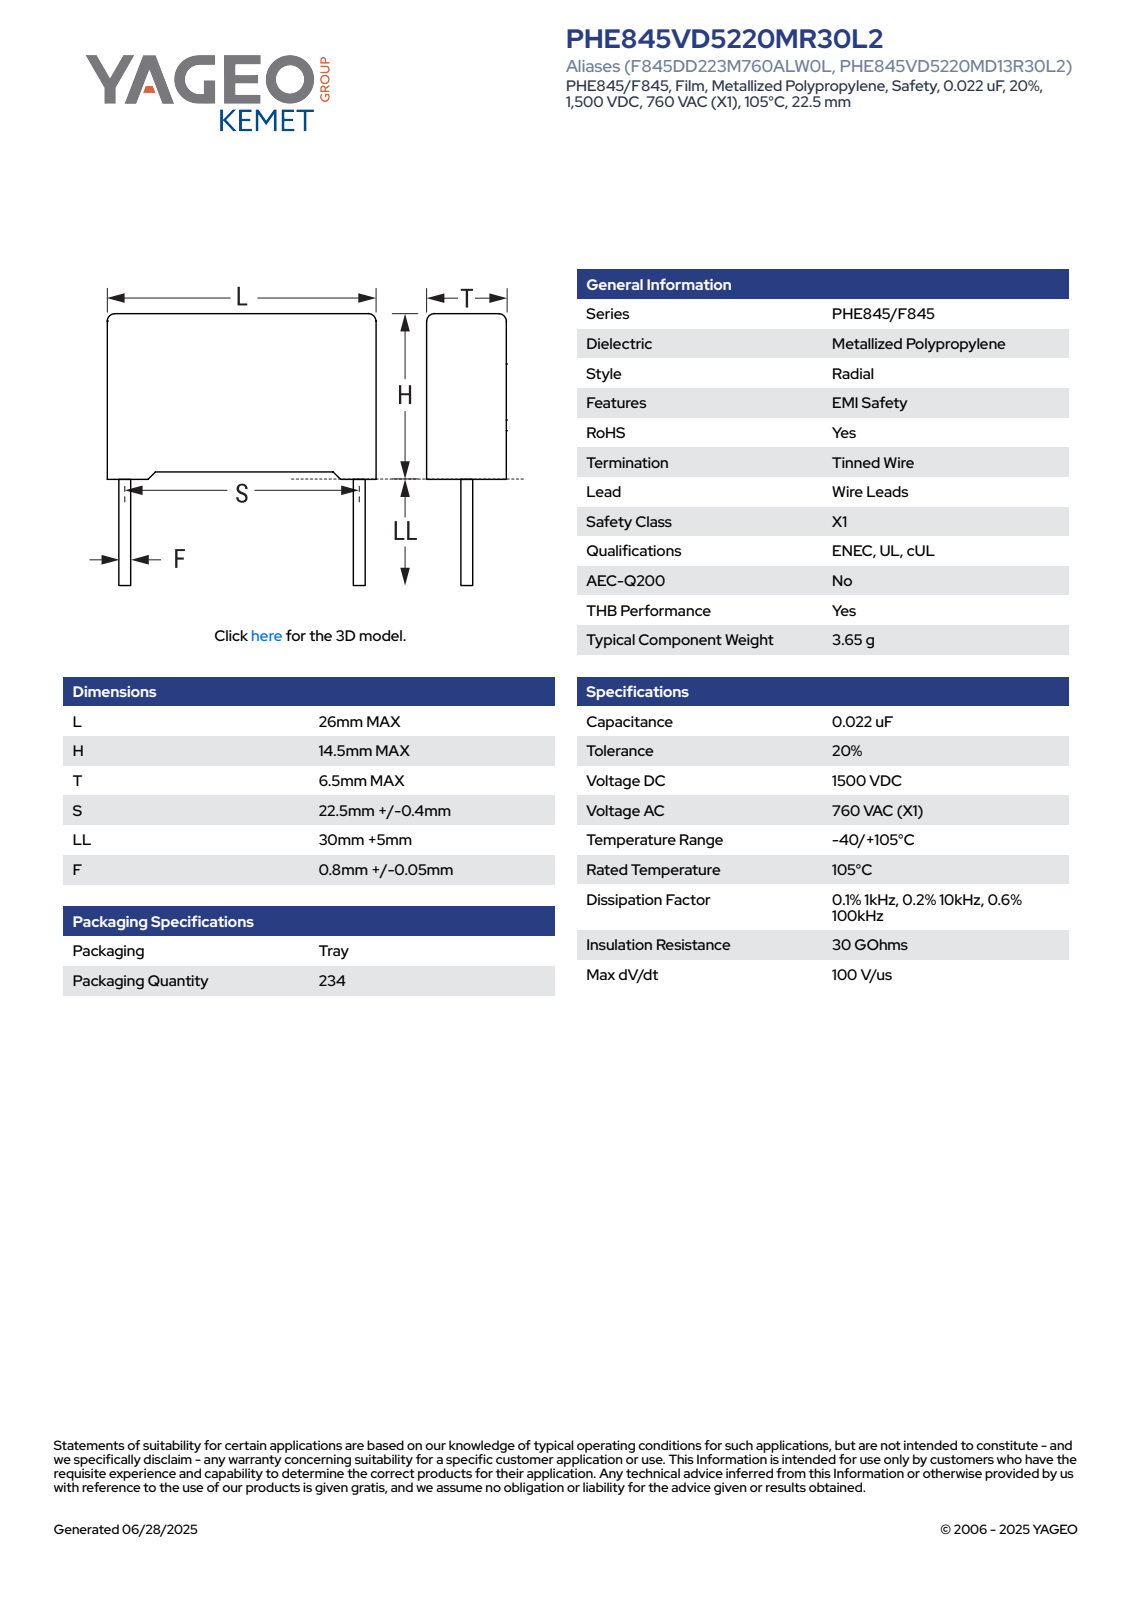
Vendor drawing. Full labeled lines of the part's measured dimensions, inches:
Part name (STEP PRODUCT): CFR_RB2_26X14.5X6.5_L26H14.5T6.5S22.5LL35F0.8
STEP written by: SolidWorks 2021 (AUTOMOTIVE_DESIGN)
Units: inches
Bodies: 4 solids, 85 faces (77 planar, 8 cylindrical, 0 other)
Overall size (bounding box): 1.949 × 1.024 × 0.256
Volume: 0.145 in³ · Surface area: 2.33 in²
Round bosses / shafts (diameter × count): ⌀0.031 ×2
Partial cylindrical surfaces — rounded edges, fillets, slot ends (radius × count): R0.02 ×4
Main face-to-face distances: 0.256, 0.541, 1.024, 0.551, 0.034, 0.02, 0.03, 0.571, 0.222, 0.187
